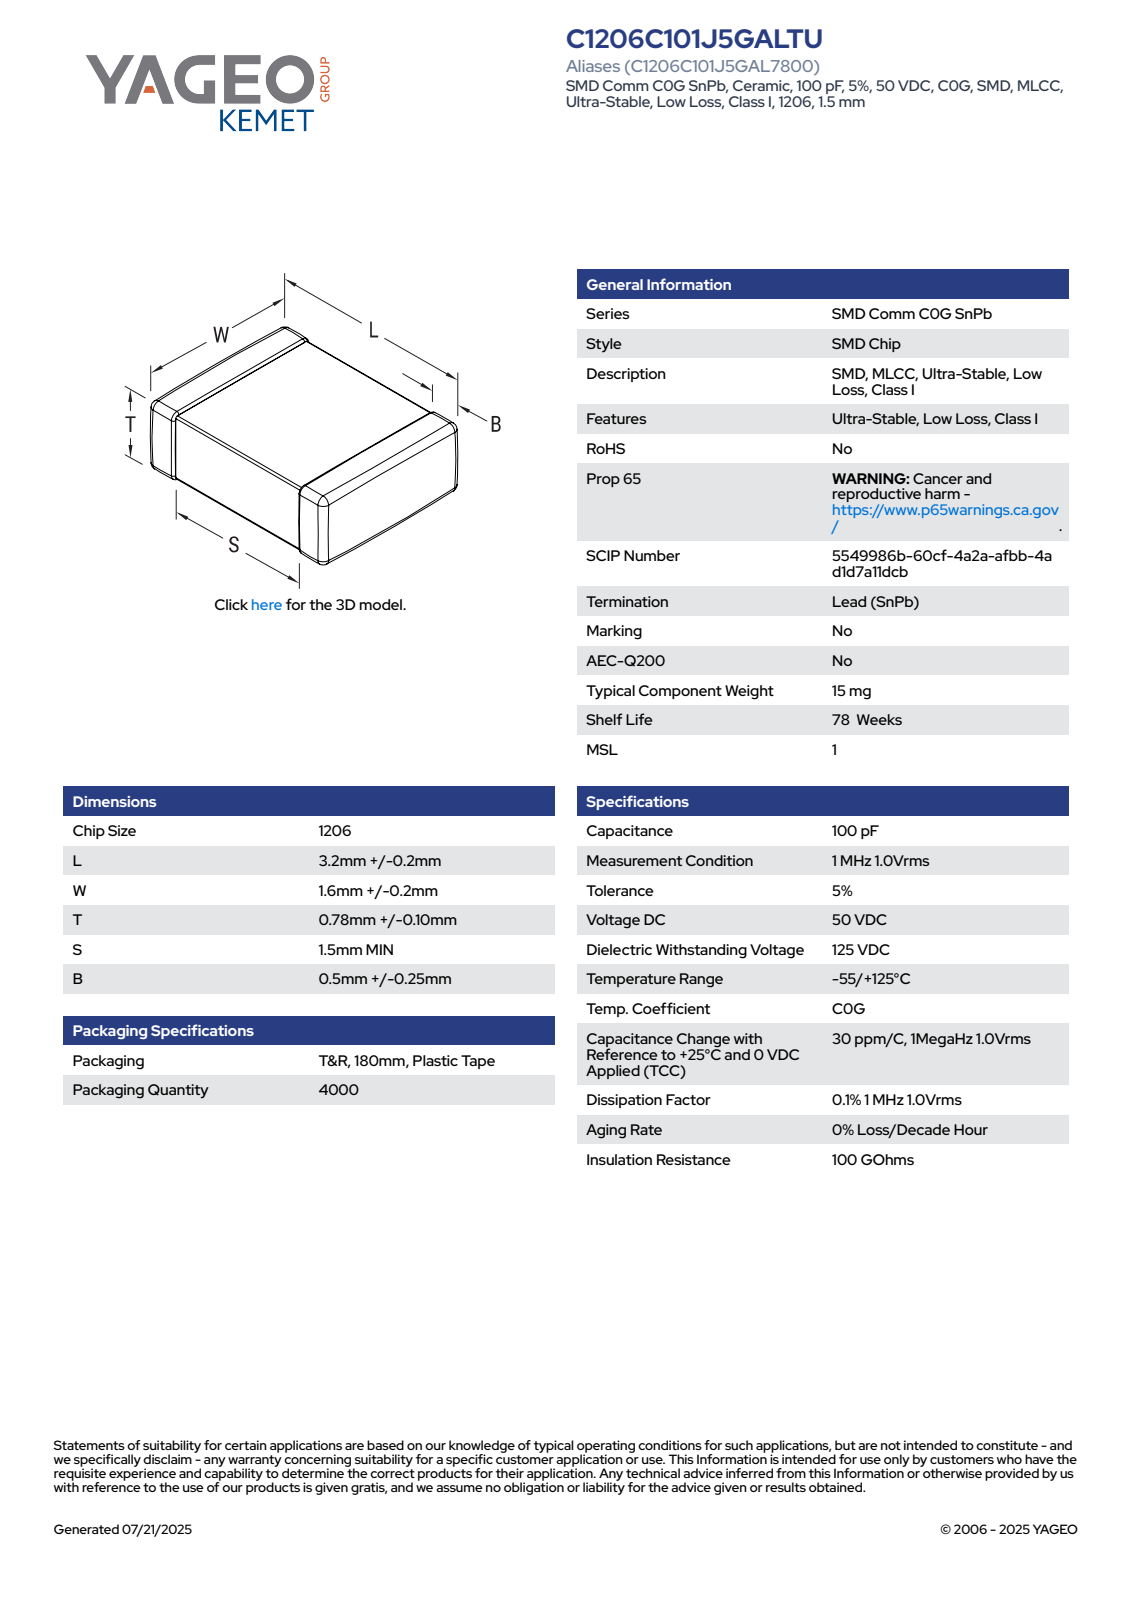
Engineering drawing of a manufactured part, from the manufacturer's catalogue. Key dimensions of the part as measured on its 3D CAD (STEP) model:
Part name (STEP PRODUCT): CCS_CCSTD_1206_L3.4W1.8T0.88B0.5
STEP written by: SolidWorks 2021 (AUTOMOTIVE_DESIGN)
Units: millimetres
Bodies: 4 solids, 125 faces (71 planar, 38 cylindrical, 16 other)
Overall size (bounding box): 3.4 × 1.8 × 0.88
Volume: 5 mm³ · Surface area: 21 mm²
Main face-to-face distances: 0.84, 0.8, 0.88, 1.76, 3.4, 1.72, 1.8, 0.85, 0.81, 1.57
